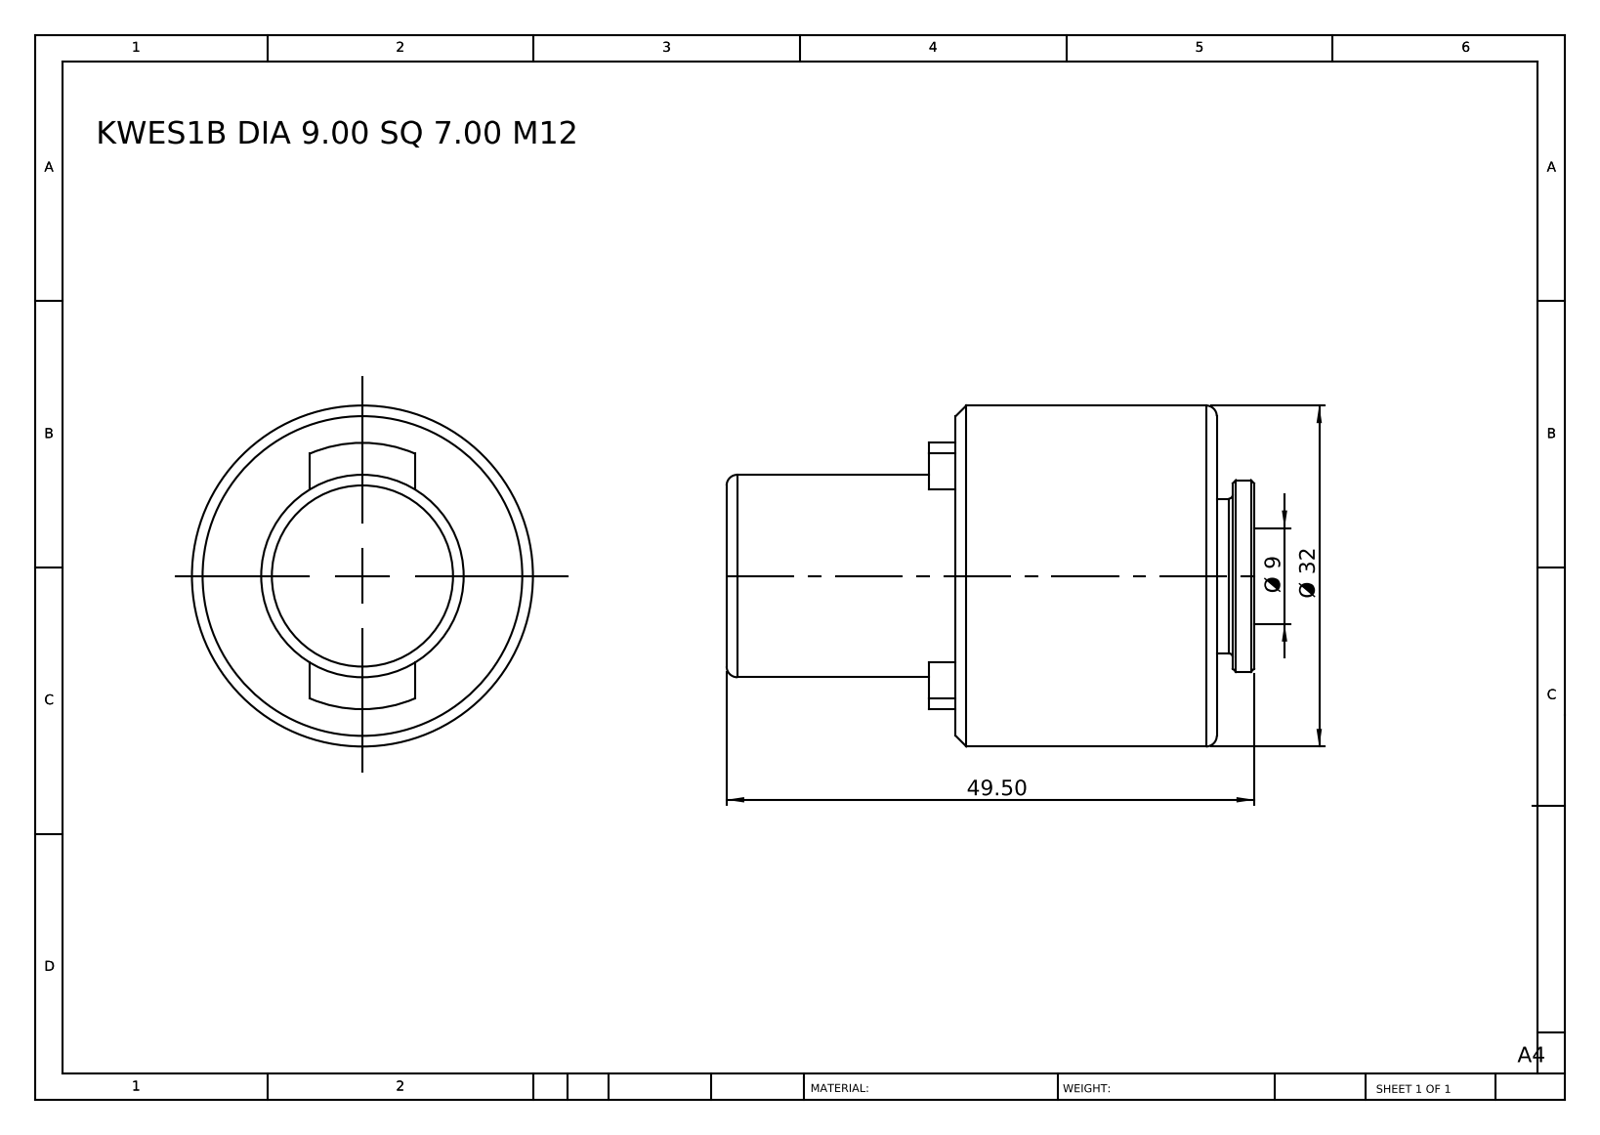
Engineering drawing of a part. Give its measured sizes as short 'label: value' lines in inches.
name: KWES1B DIA 9.00 SQ 7.00 1-2'''''''' UNC
written by: SolidWorks 2014 (CONFIG_CONTROL_DESIGN)
unit: in
bodies: 1 solid, 39 faces (12 planar, 13 cylindrical, 14 other)
size: 1.949 × 1.26 × 1.26
volume: 1.57 in³; area: 9.266 in²
holes: 1× ⌀0.354
bosses: 1× ⌀1.26, 1× ⌀0.748, 1× ⌀0.709, 1× ⌀0.571
rounds: 1× R0.492
face distances: 0.965, 0.846, 1.811, 1.949, 1.102, 0.138, 0.551, 1.398, 0.413, 0.748
